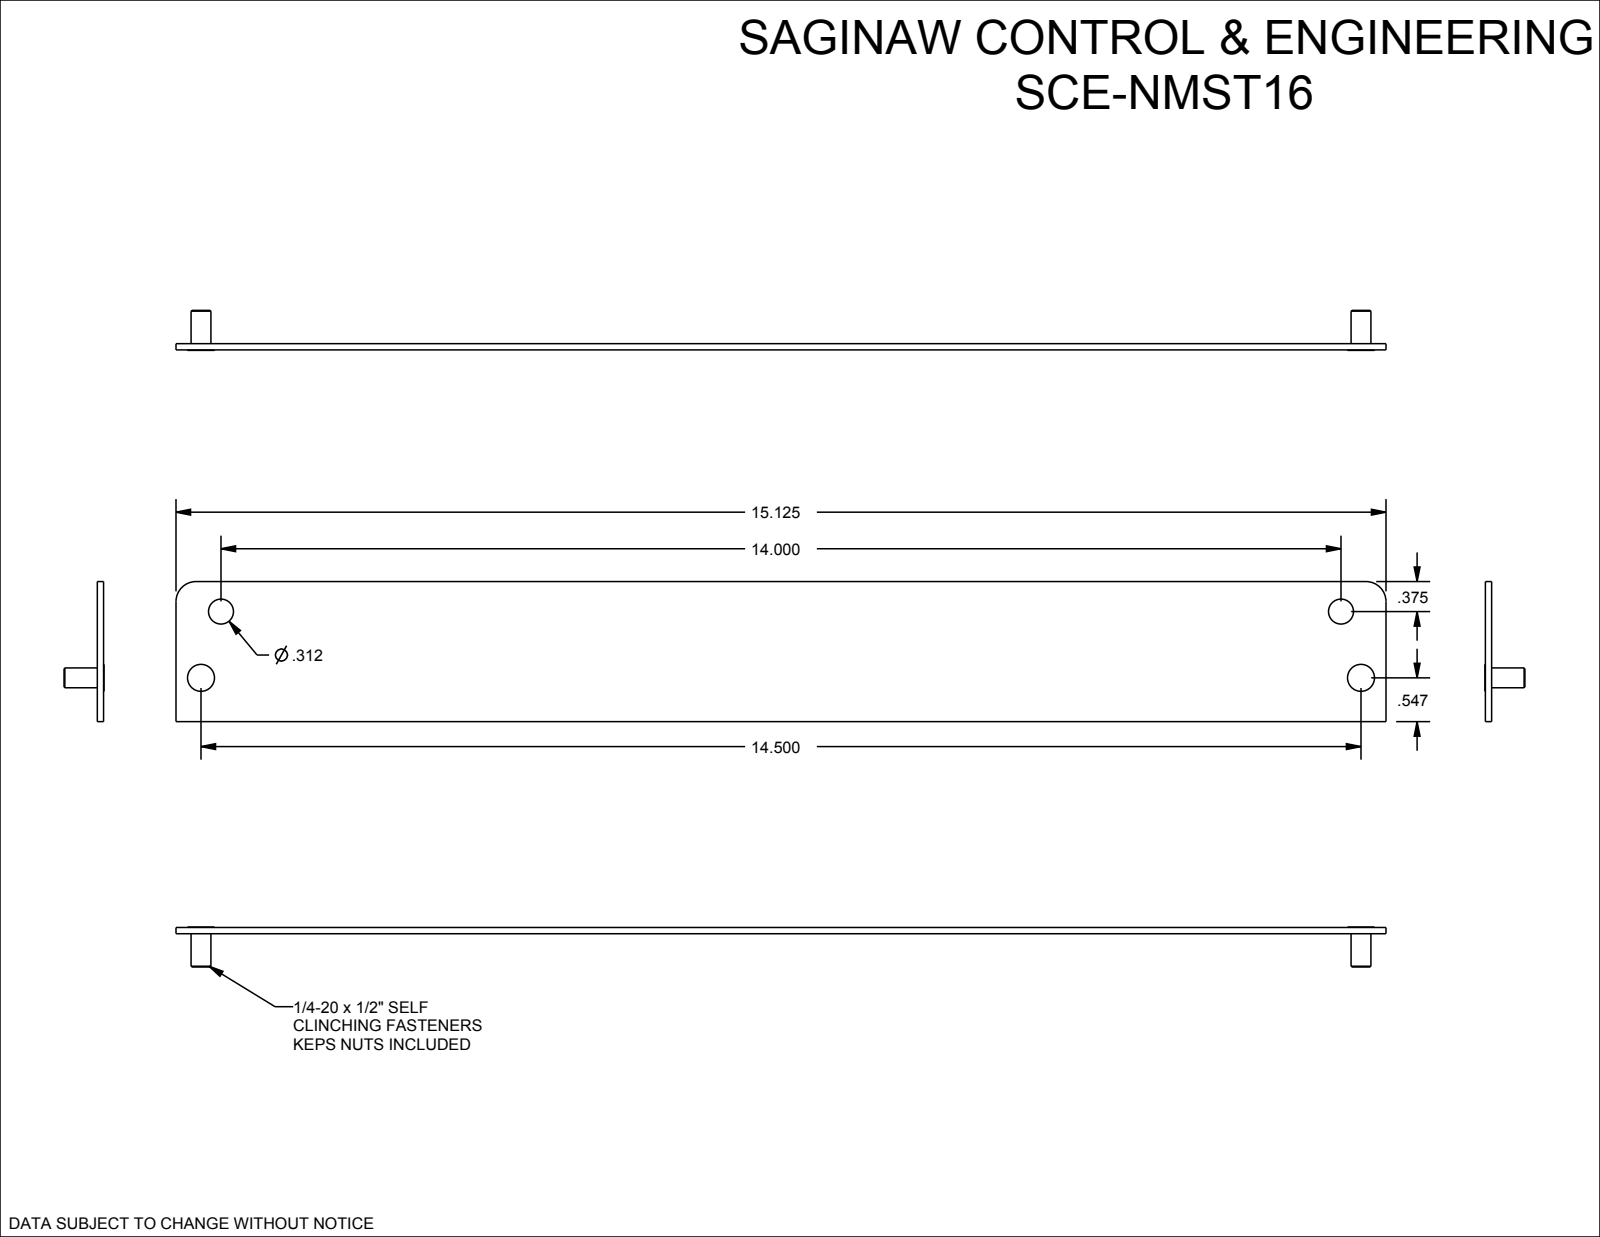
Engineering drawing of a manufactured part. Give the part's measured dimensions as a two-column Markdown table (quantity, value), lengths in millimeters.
| quantity | value |
| --- | --- |
| part name | SCE-NMST16 |
| STEP written by | SolidWorks 2019 (AUTOMOTIVE_DESIGN) |
| units | millimeters |
| bodies | 3 solids, 24 faces (12 planar, 10 cylindrical, 2 other) |
| overall size | 384.2 × 44.5 × 12.7 |
| volume | 34 300 mm³ |
| surface area | 36 390 mm² |
| round holes (diameter × count) | 6.4 × 2, 7.9 × 2 |
| round bosses / shafts (diameter × count) | 8.6 × 2, 6.3 × 2 |
| partial cylindrical surfaces (radius × count) | 6.4 × 2 |
| main face-to-face distances | 2, 44.5, 2.1, 384.2, 1.7, 0.5, 10.6, 12.2, 12.5, 12.7 |
| hole center spacings | 22, 362.6, 355.6, 368.3 |
